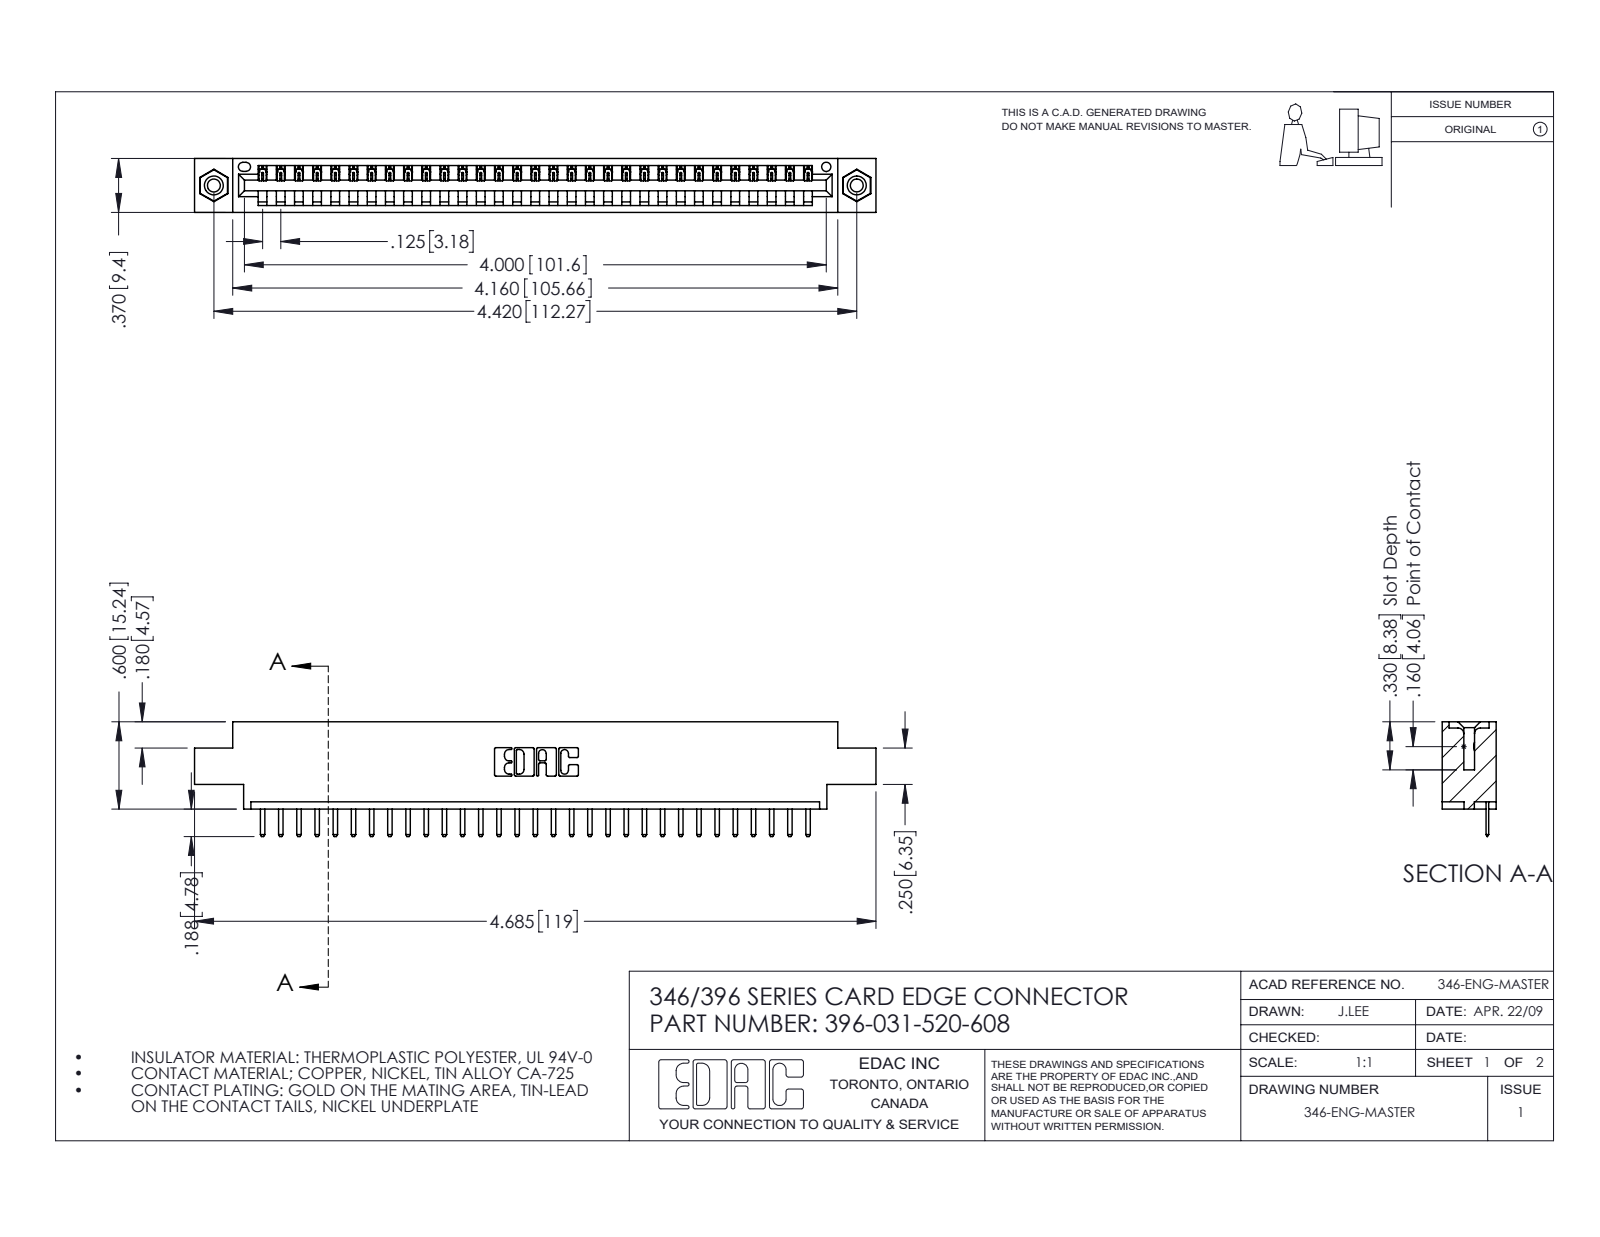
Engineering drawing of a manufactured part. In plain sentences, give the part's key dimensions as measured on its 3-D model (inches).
The part is named "396-031-520-608; 345-292-001_345-293-120; 346 Part_0.170 Offset - 0.156 Dia-TI; 345-250-001_345-250-003-102". Its 3-D file was written by "SolidWorks 2016 (CONFIG_CONTROL_DESIGN)". It is 34 solids with 2108 faces: 1414 planar, 678 cylindrical and 16 other. Overall it measures 4.685 by 0.788 by 0.37 inches. Its volume is 0.675 cubic inches and its surface area 21.07 square inches. Round holes: 2 of diameter 0.089, 2 of diameter 0.125, 2 of diameter 0.156, 1 of diameter 0.064. Round bosses or shafts: 2 of diameter 0.155. Partial cylindrical surfaces (rounded edges, fillets, slot ends): 64 of radius 0.01, 62 of radius 0.006, 22 of radius 0.01, 6 of radius 0.007, 6 of radius 0.031, 3 of radius 0.026, 2 of radius 0.031, 2 of radius 0.04. The main face-to-face distances are 0.048, 0.322, 0.37, 0.25, 0.222, 0.148, 0.1, 0.174, 0.072, 0.298. The hole center spacings are 0.246, 4.212, 4.42.
